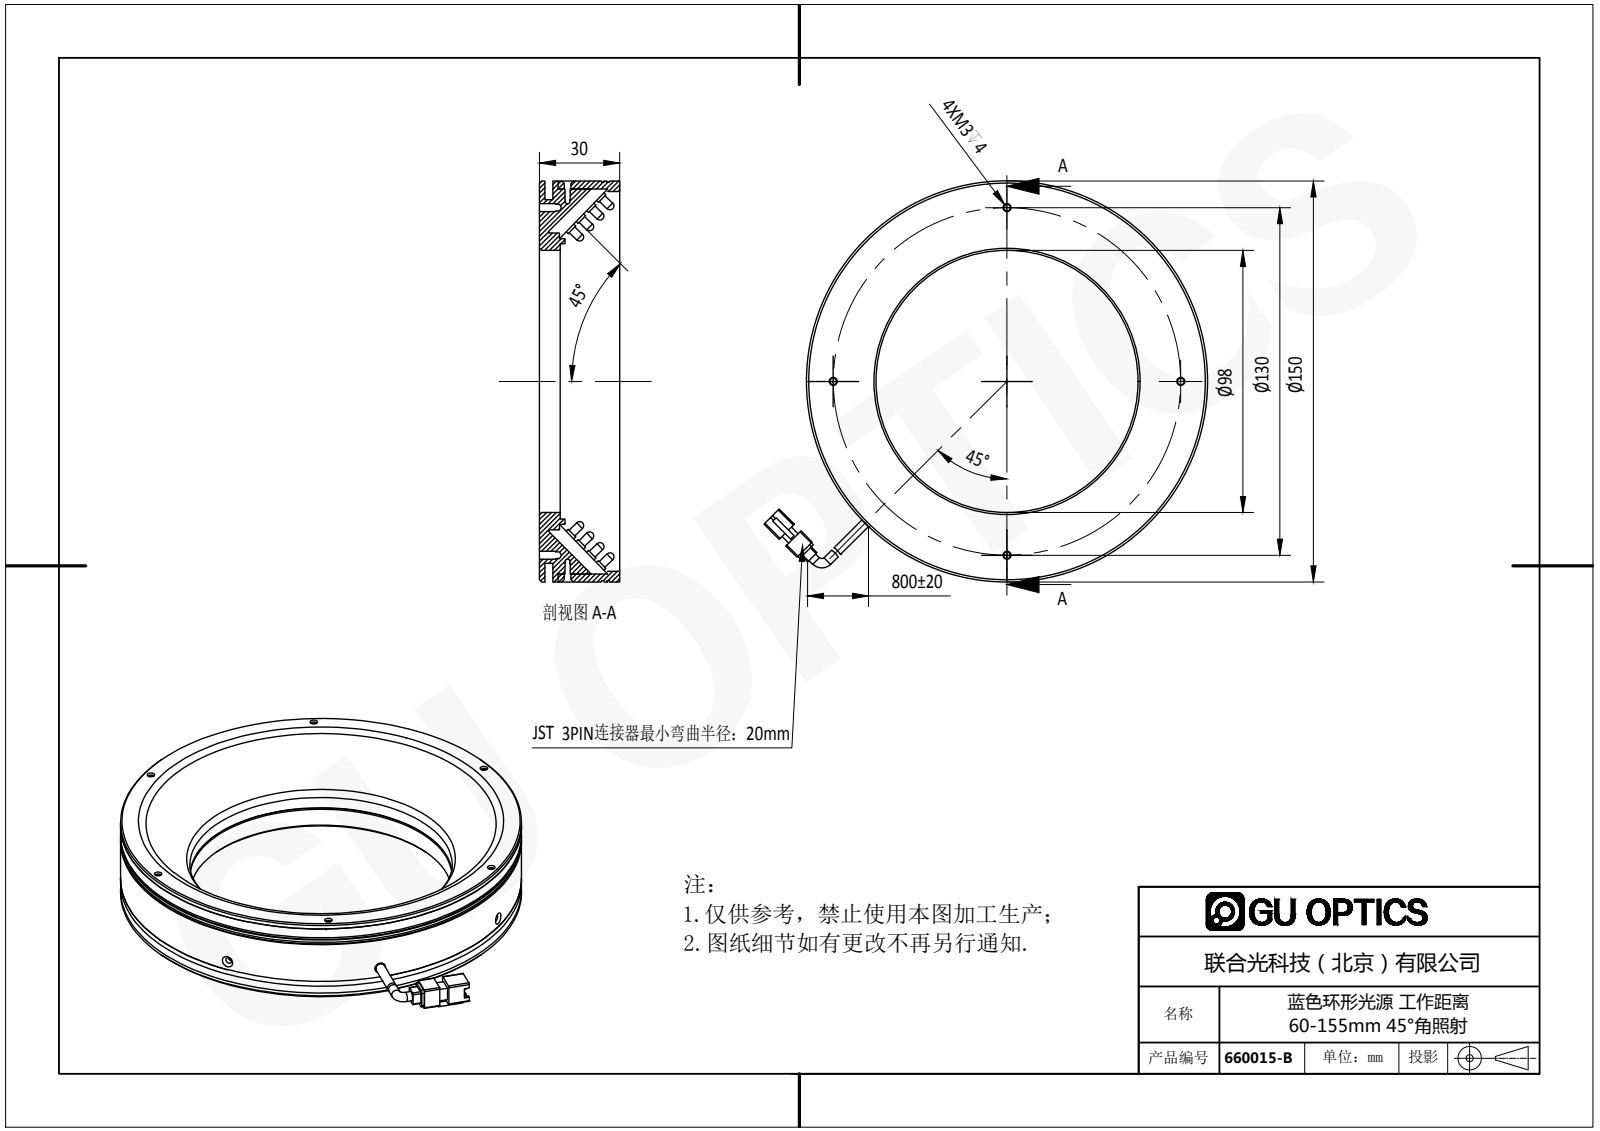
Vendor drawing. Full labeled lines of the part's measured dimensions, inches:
Part name (STEP PRODUCT): 660015-B
STEP written by: SolidWorks 2016 (AUTOMOTIVE_DESIGN)
Units: inches
Bodies: 326 solids, 5782 faces (3937 planar, 1453 cylindrical, 392 other)
Overall size (bounding box): 6.53 × 5.906 × 1.26
Volume: 10.48 in³ · Surface area: 227.4 in²
Round holes (diameter × count): ⌀0.043 ×6, ⌀0.055 ×6, ⌀0.059 ×6, ⌀0.11 ×6, ⌀0.098 ×4, ⌀0.118 ×4, ⌀0.138 ×4, ⌀0.063 ×2, ⌀0.079 ×2, ⌀0.094 ×2, ⌀0.142 ×1, ⌀3.858 ×1
Round bosses / shafts (diameter × count): ⌀0.15 ×320, ⌀0.118 ×320, ⌀0.138 ×2, ⌀5.906 ×1, ⌀5.866 ×1, ⌀5.669 ×1, ⌀5.354 ×1, ⌀4.37 ×1
Partial cylindrical surfaces — rounded edges, fillets, slot ends (radius × count): R0.02 ×12, R0.039 ×4, R0.315 ×1
Main face-to-face distances: 0.079, 1.181, 0.197, 0.984, 0.118, 0.276, 1.102, 0.906, 0.02, 1.26
Hole centre spacings: 2.835, 4.91, 0.74, 5.238, 1.421, 2.08, 2.17, 2.559
